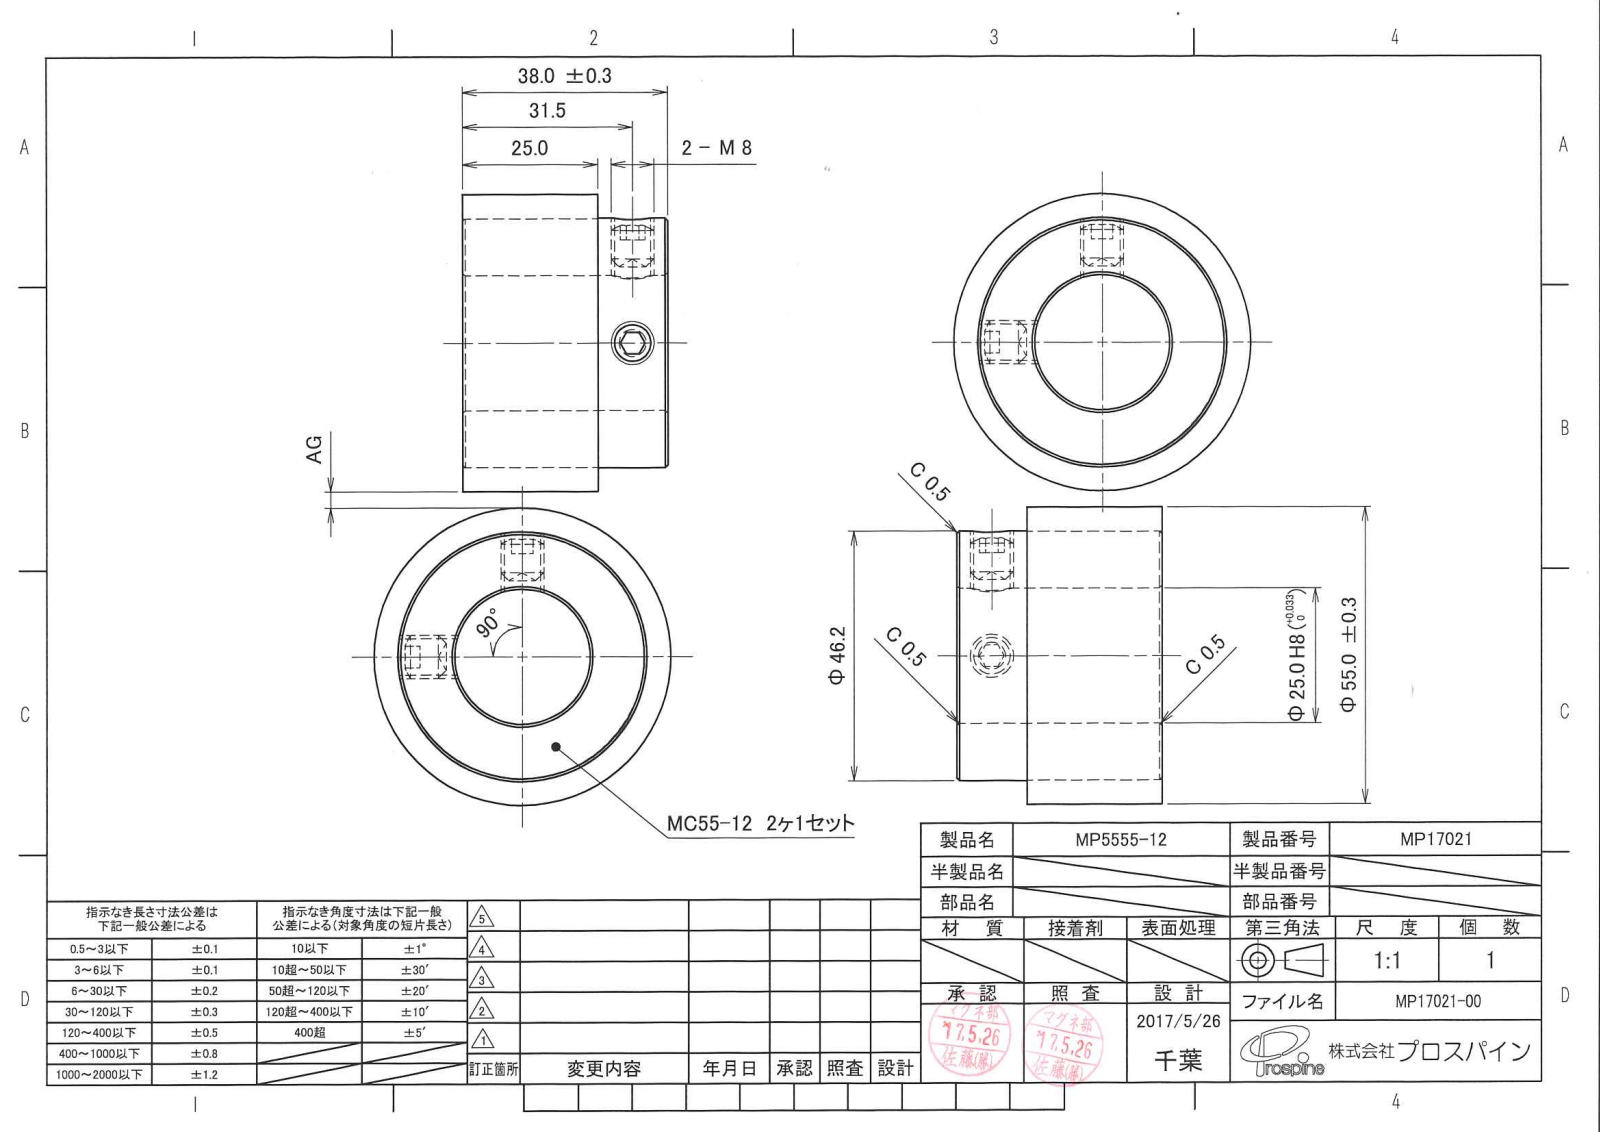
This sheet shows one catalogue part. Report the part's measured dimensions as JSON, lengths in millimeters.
{"step_written_by": "PSStep 10.0 (CONFIG_CONTROL_DESIGN)", "units": "millimeters", "bodies": {"solids": 10, "faces": 98, "planar": 52, "cylindrical": 20, "other": 26}, "overall_size": [113, 55, 55], "volume_mm3": 125214, "surface_area_mm2": 42529, "round_holes": [[6.75, 4], [25, 2], [46, 2]], "round_bosses_or_shafts": [[8, 5], [55, 2], [46.2, 2]], "face_to_face_distances": [38, 13, 25, 4, 21.07, 17.07, 46.07, 33.07, 8.07, 58], "hole_center_spacings": [61.52, 28.99]}
